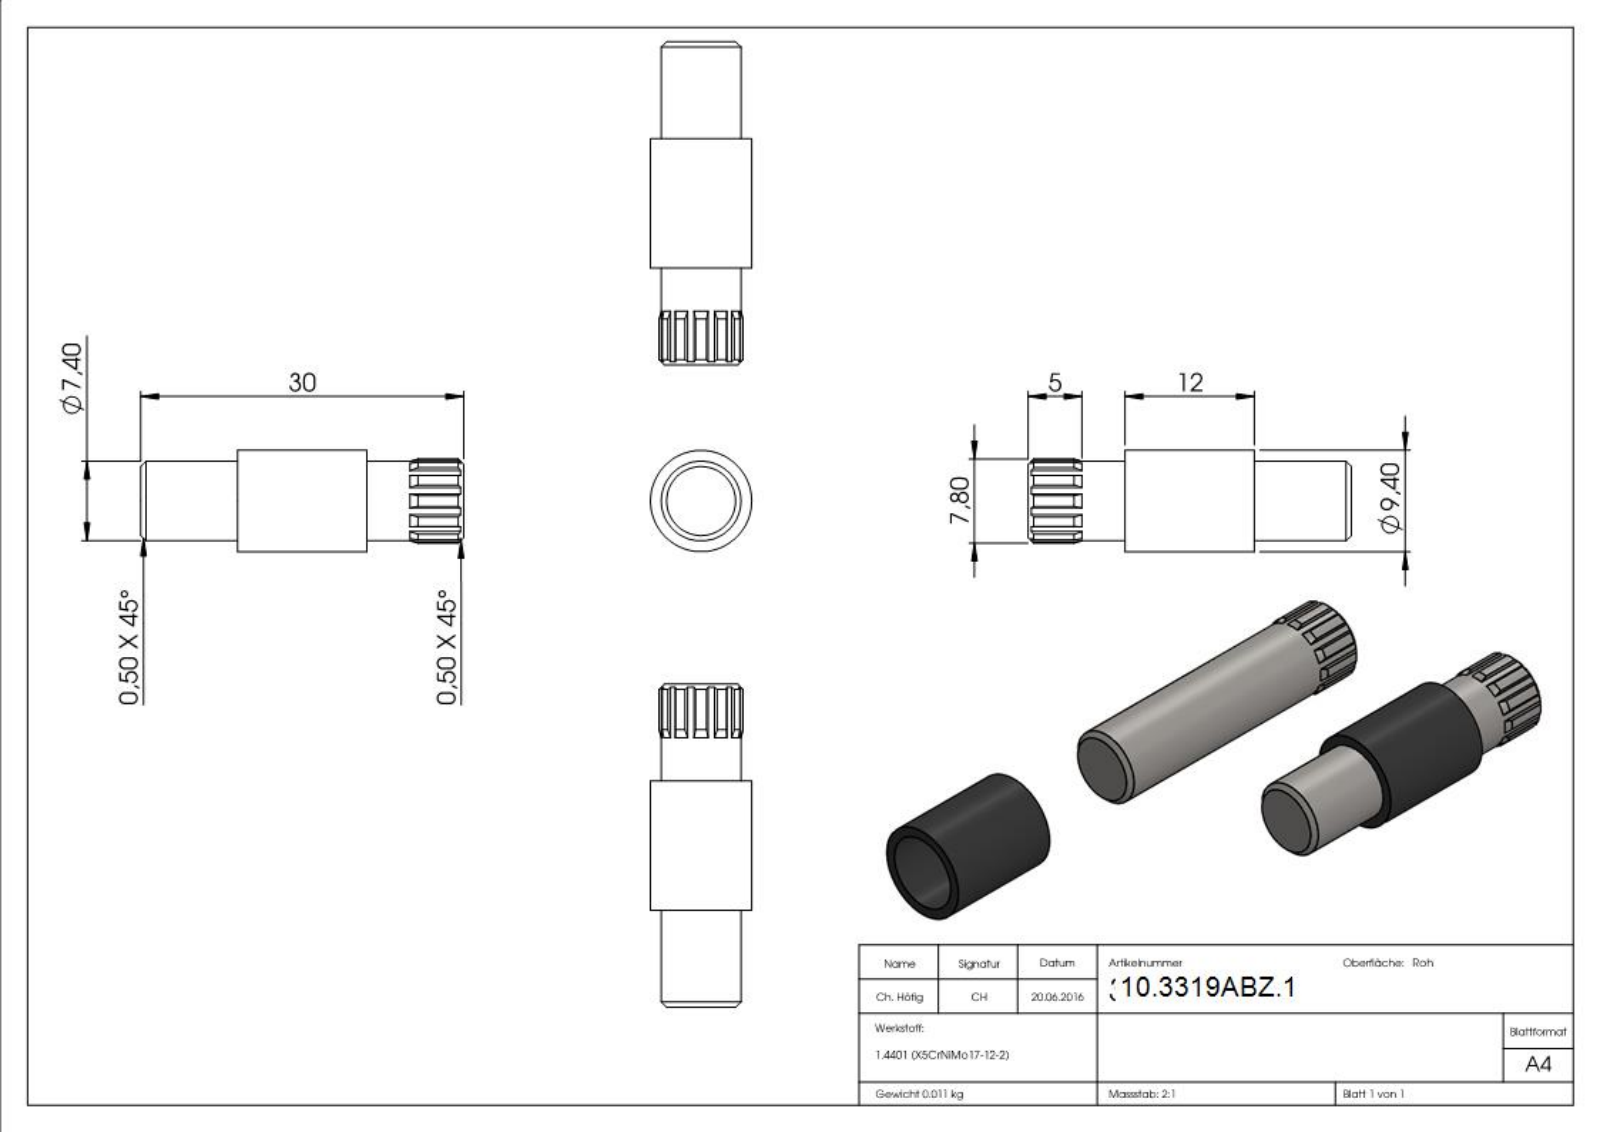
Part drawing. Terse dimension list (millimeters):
name: 39-Stift; 39-Stift Teil2; 39-Stift Teil1
written by: SolidWorks 2015 (CONFIG_CONTROL_DESIGN)
unit: mm
bodies: 2 solids, 285 faces (155 planar, 19 cylindrical, 111 other)
size: 30 × 9.4 × 9.4
volume: 1 615 mm³; area: 1 475 mm²
holes: 1× ⌀7.4
bosses: 1× ⌀9.4
rounds: 1× R3.9
face distances: 9, 21, 30, 12, 5.12, 5.11, 8.9, 20.9, 29.9, 0.81
